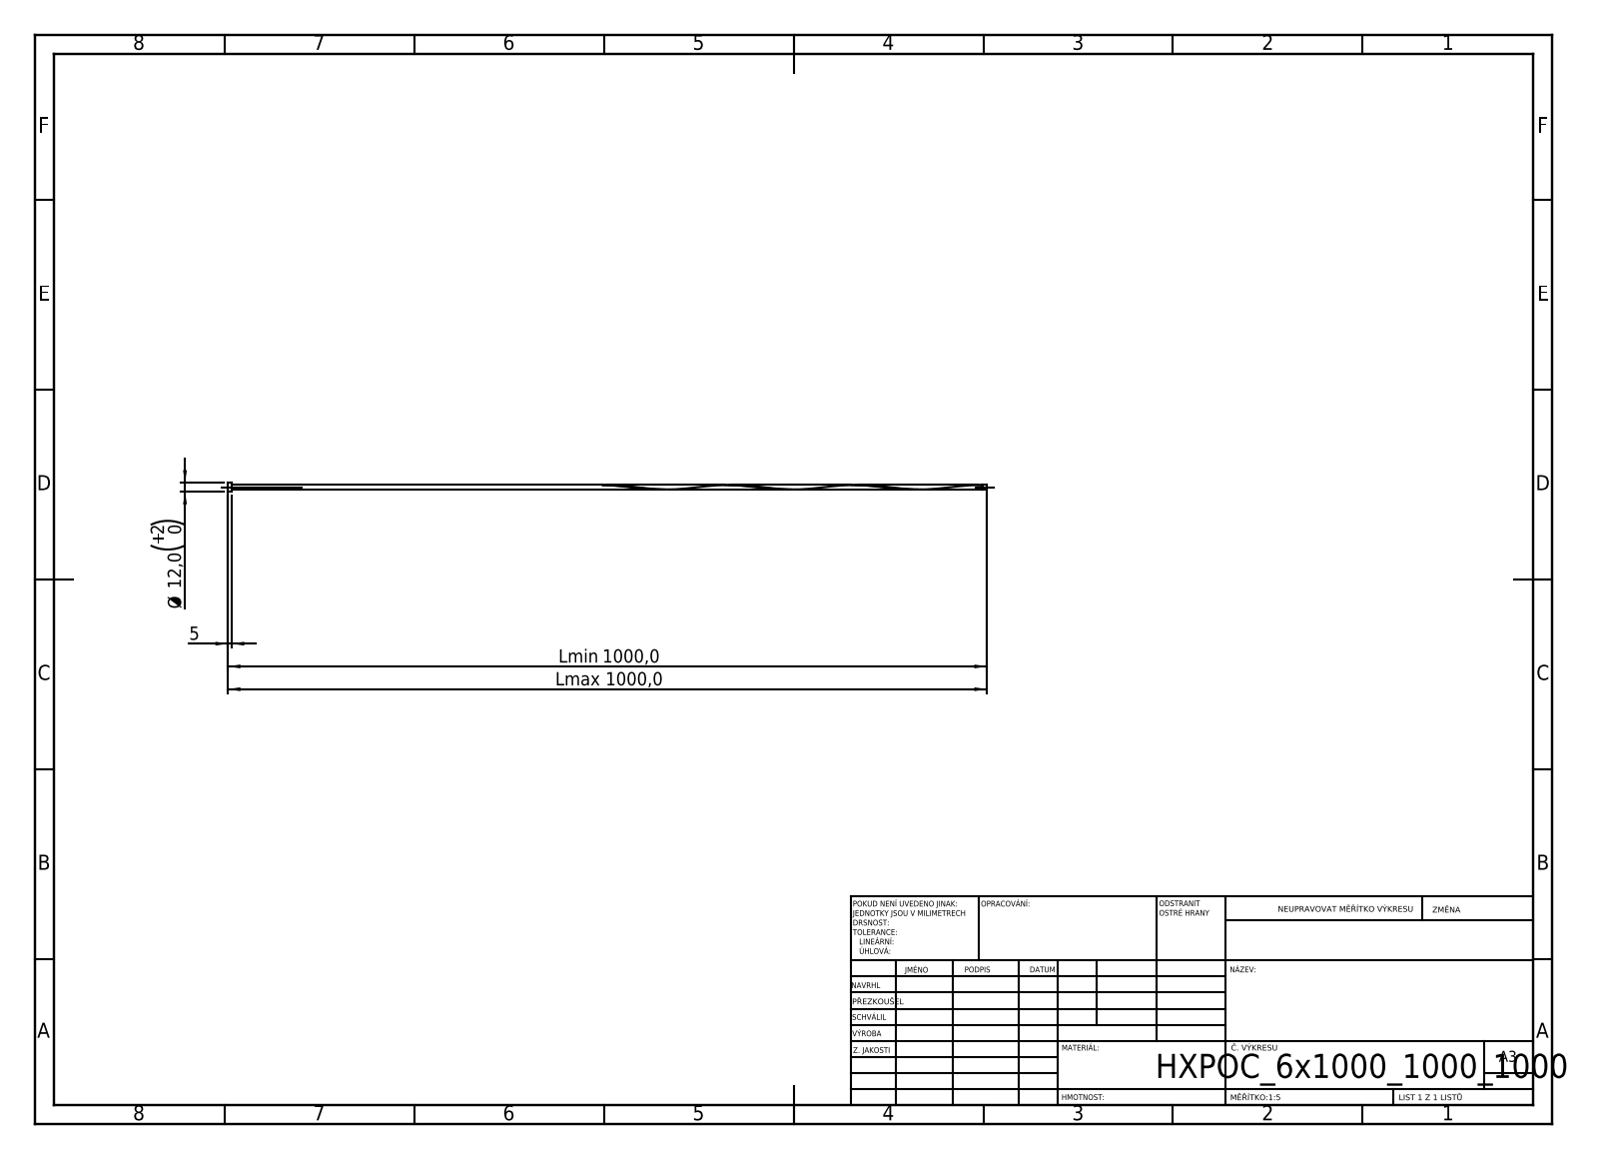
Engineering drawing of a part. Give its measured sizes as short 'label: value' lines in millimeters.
written by: SolidWorks 2019 (CONFIG_CONTROL_DESIGN)
unit: mm
bodies: 1 solid, 16 faces (6 planar, 9 cylindrical, 1 other)
size: 1000 × 12 × 12
volume: 34 699 mm³; area: 25 753 mm²
bosses: 1× ⌀12, 1× ⌀6, 1× ⌀4.8
face distances: 5, 1000, 995, 994.08, 989.08, 5.92, 992.88, 987.88, 1.2, 7.12
